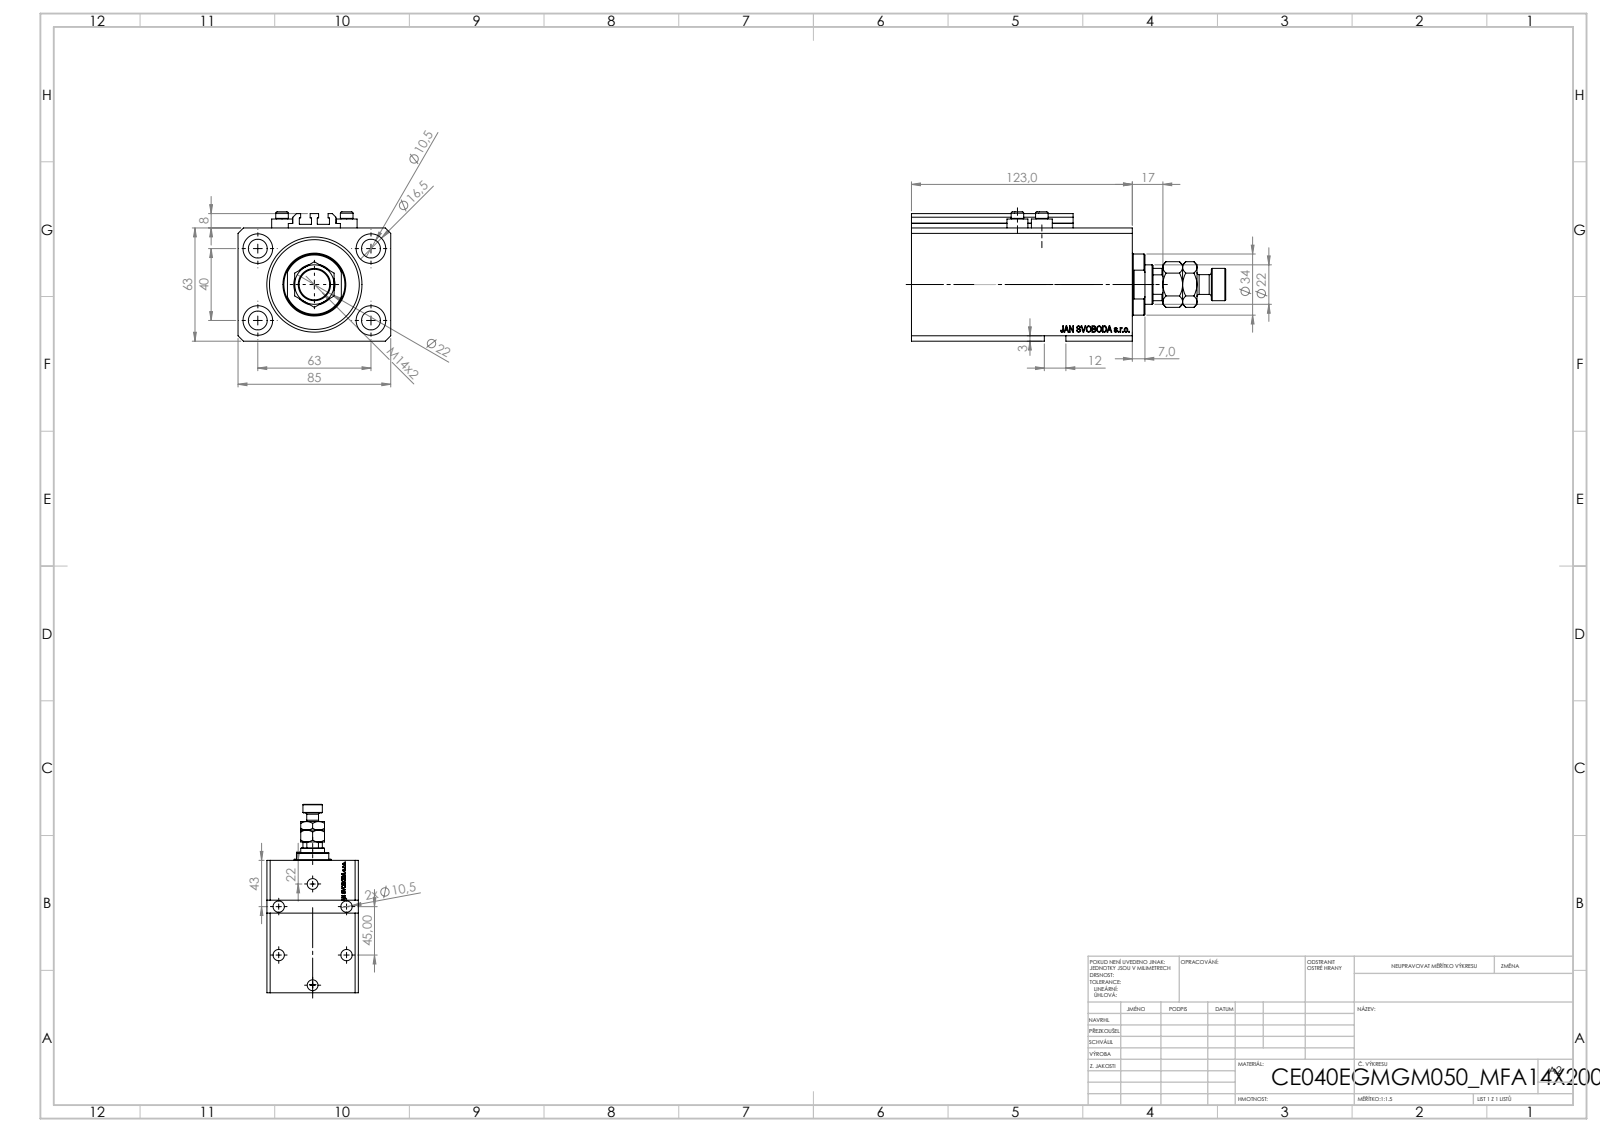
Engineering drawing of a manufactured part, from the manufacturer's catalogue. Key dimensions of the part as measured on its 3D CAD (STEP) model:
Part name (STEP PRODUCT): V250CE_VC_E; ALLEN BOLT V250CE; V250CE_C_VCP; V250CE_E_Body (+1 more)
STEP written by: SolidWorks 2019 (CONFIG_CONTROL_DESIGN)
Units: millimetres
Bodies: 9 solids, 1159 faces (551 planar, 150 cylindrical, 458 other)
Overall size (bounding box): 175 × 85 × 72
Volume: 567 327 mm³ · Surface area: 122 558 mm²
Round holes (diameter × count): ⌀10.5 ×8, ⌀1.25 ×4, ⌀4 ×4, ⌀16.5 ×4, ⌀10 ×2, ⌀13.16 ×2, ⌀20 ×2, ⌀12.5 ×1, ⌀22 ×1, ⌀40 ×1, ⌀53 ×1
Round bosses / shafts (diameter × count): ⌀11.6 ×4, ⌀7 ×4, ⌀34 ×1, ⌀18 ×1, ⌀11 ×1
Partial cylindrical surfaces — rounded edges, fillets, slot ends (radius × count): R0.2 ×10, R10.5 ×1
Main face-to-face distances: 63, 85, 17, 123, 106, 11.4, 94.6, 111.6, 3, 56
Hole centre spacings: 37.31, 63, 13.6, 15.4, 24.96, 27.54, 33.62, 36
